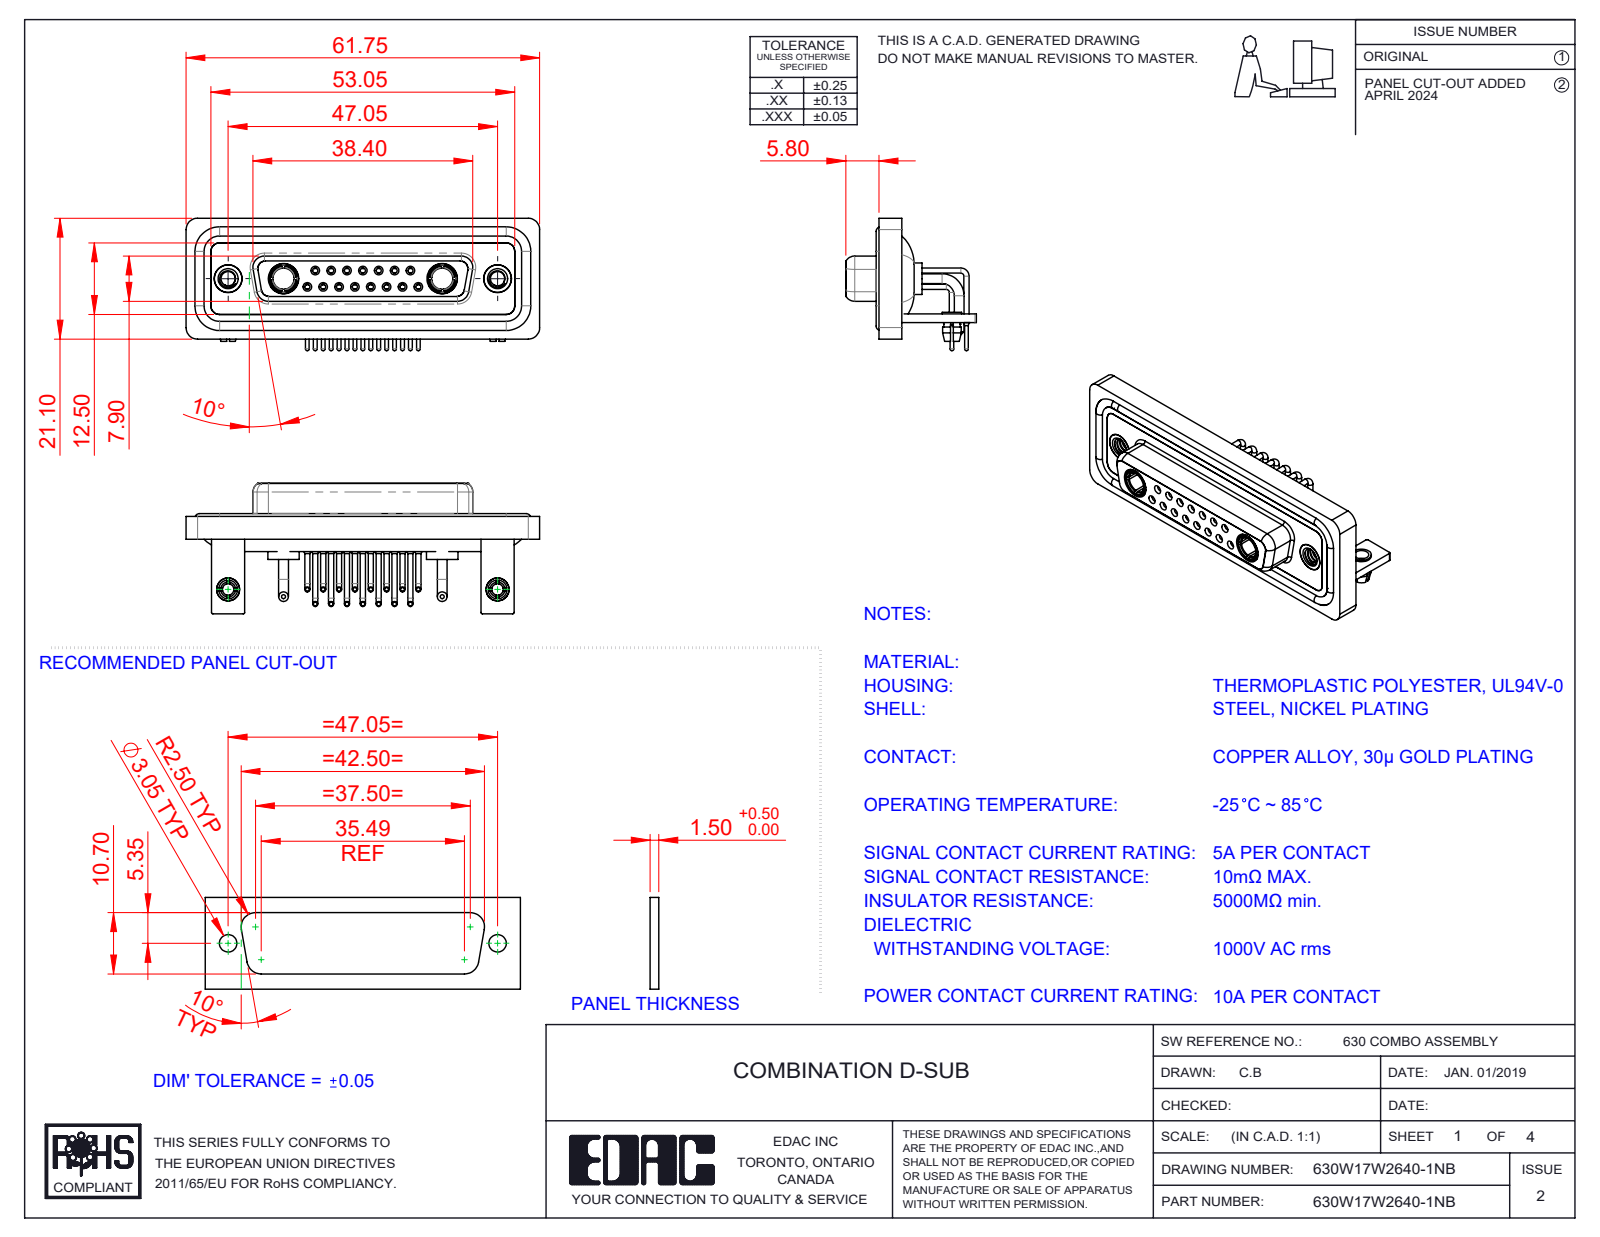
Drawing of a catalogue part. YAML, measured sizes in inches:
part_name: "630Combo Shell Front_25 Contacts; 630Combo Contact Row 1_50 Contacts; 630Combo Threaded Rivet_A; 630W17W2640-1NB (+7 more)"
step_written_by: "SolidWorks 2023 (CONFIG_CONTROL_DESIGN)"
units: inches
bodies: {solids: 30, faces: 1471, planar: 456, cylindrical: 637, other: 378}
overall_size: [2.431, 0.91, 0.898]
volume: 0.535
surface_area: 23.84
round_holes:
  - {diameter: 0.079, count: 17}
  - {diameter: 0.035, count: 15}
  - {diameter: 0.043, count: 15}
  - {diameter: 0.059, count: 15}
  - {diameter: 0.063, count: 8}
  - {diameter: 0.067, count: 7}
  - {diameter: 0.098, count: 4}
  - {diameter: 0.191, count: 4}
  - {diameter: 0.126, count: 2}
  - {diameter: 0.146, count: 2}
  - {diameter: 0.157, count: 2}
  - {diameter: 0.159, count: 2}
round_bosses_or_shafts:
  - {diameter: 0.035, count: 15}
  - {diameter: 0.026, count: 15}
  - {diameter: 0.063, count: 11}
  - {diameter: 0.067, count: 4}
  - {diameter: 0.217, count: 2}
  - {diameter: 0.205, count: 2}
  - {diameter: 0.195, count: 2}
  - {diameter: 0.195, count: 2}
partial_cylinders:
  - {radius: 0.079, count: 19}
  - {radius: 0.059, count: 18}
  - {radius: 0.01, count: 16}
  - {radius: 0.053, count: 8}
  - {radius: 0.063, count: 8}
  - {radius: 0.02, count: 5}
  - {radius: 0.024, count: 4}
  - {radius: 0.026, count: 4}
face_to_face_distances: [0.016, 0.071, 0.114, 0.059, 0.146, 0.161, 0.043, 0.055, 0.063, 0.122]
hole_center_spacings: [0.124, 0.109, 0.218, 0.327, 0.198, 0.295, 0.436, 0.198]
